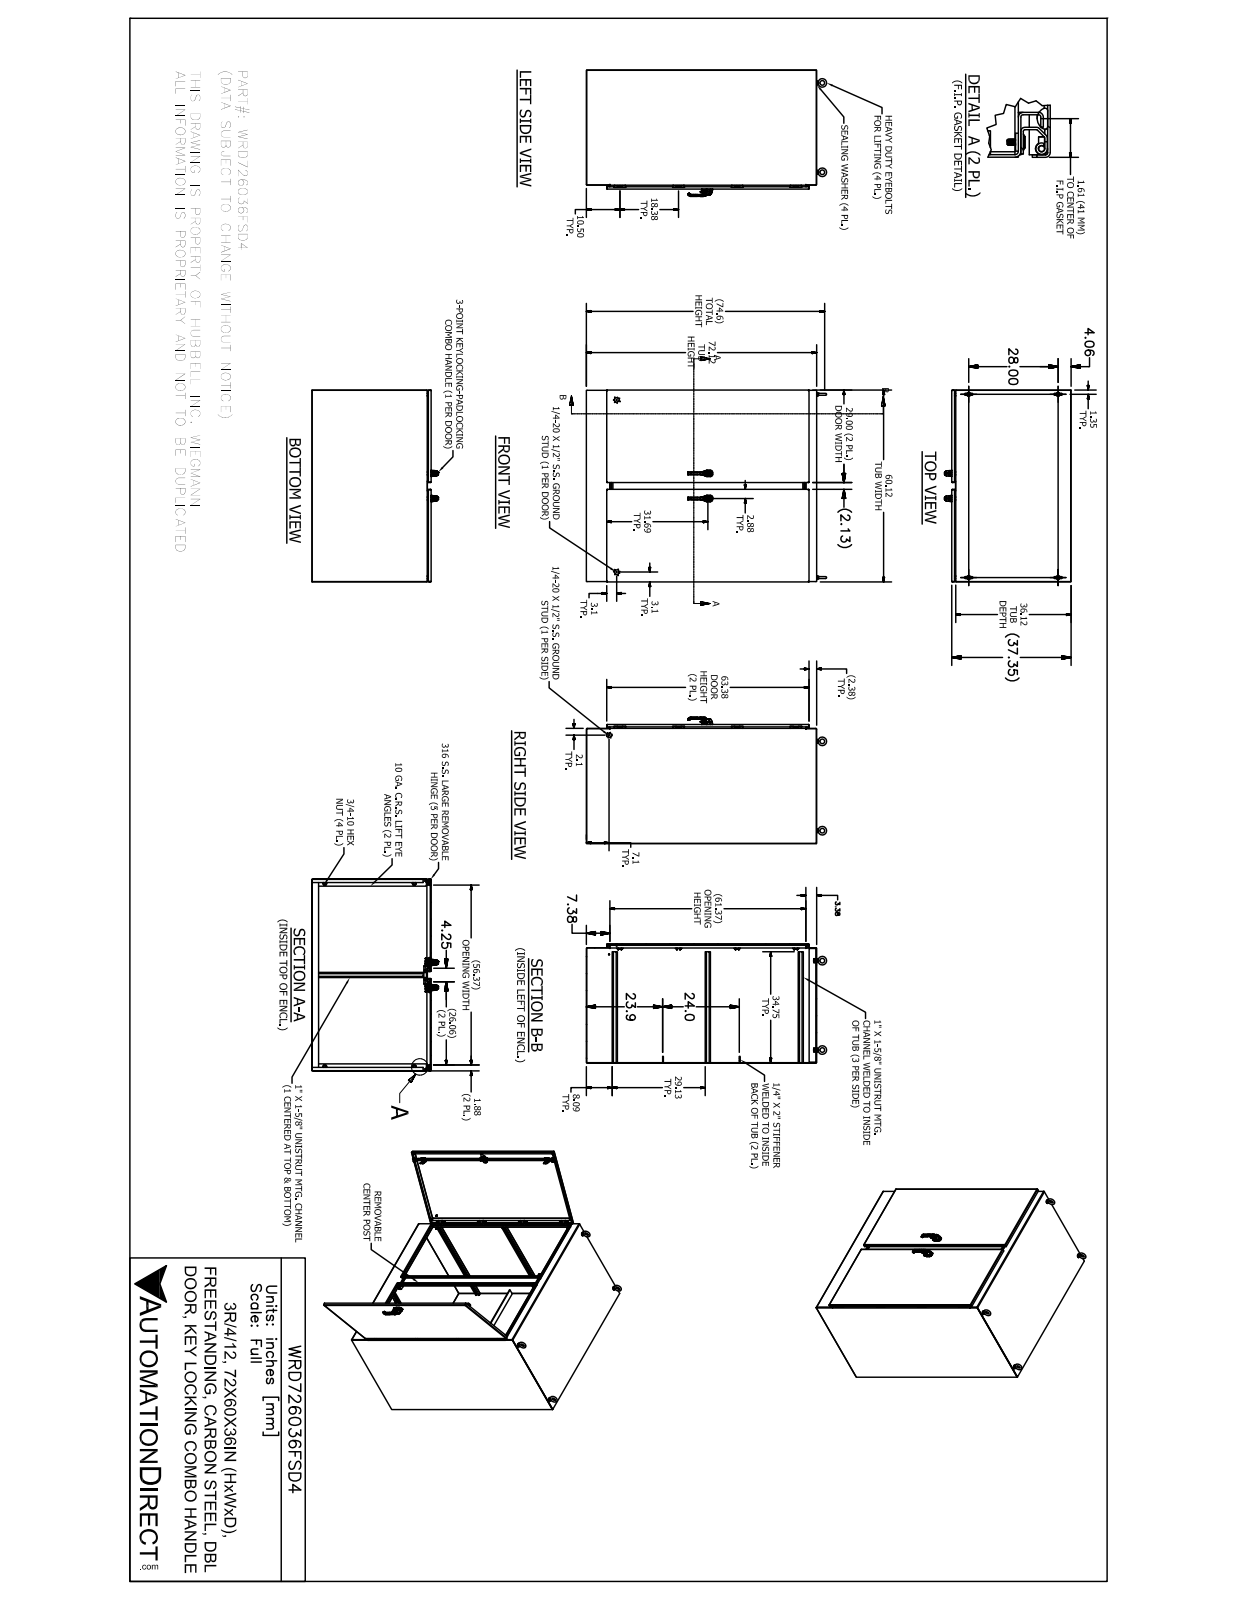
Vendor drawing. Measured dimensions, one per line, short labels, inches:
name: WRD726036FSD4
written by: SolidWorks 2017 (AUTOMOTIVE_DESIGN)
unit: in
bodies: 163 solids, 3428 faces (1552 planar, 1124 cylindrical, 752 other)
size: 75.248 × 60.133 × 39.527
volume: 2 427 in³; area: 44 513 in²
holes: 20× ⌀0.266, 16× ⌀0.23, 16× ⌀0.281, 16× ⌀0.65, 8× ⌀0.2, 8× ⌀0.277, 6× ⌀0.281, 4× ⌀0.156, 4× ⌀0.252, 4× ⌀0.4, 4× ⌀0.45, 4× ⌀0.642
bosses: 13× ⌀0.25, 10× ⌀0.625, 6× ⌀0.625, 4× ⌀1.25, 4× ⌀1.12, 4× ⌀0.75, 4× ⌀0.533, 4× ⌀0.438
rounds: 50× R0.062, 32× R0.05, 32× R0.125, 16× R0.01, 16× R0.019, 16× R0.025, 16× R0.053, 16× R0.067
face distances: 0.104, 37.245, 60.021, 72.021, 37.141, 37.349, 59.917, 60.125, 71.917, 72.125
hole spacings: 61.676, 1, 18.375, 36.75, 58.875, 58.884, 69.404, 61.385
